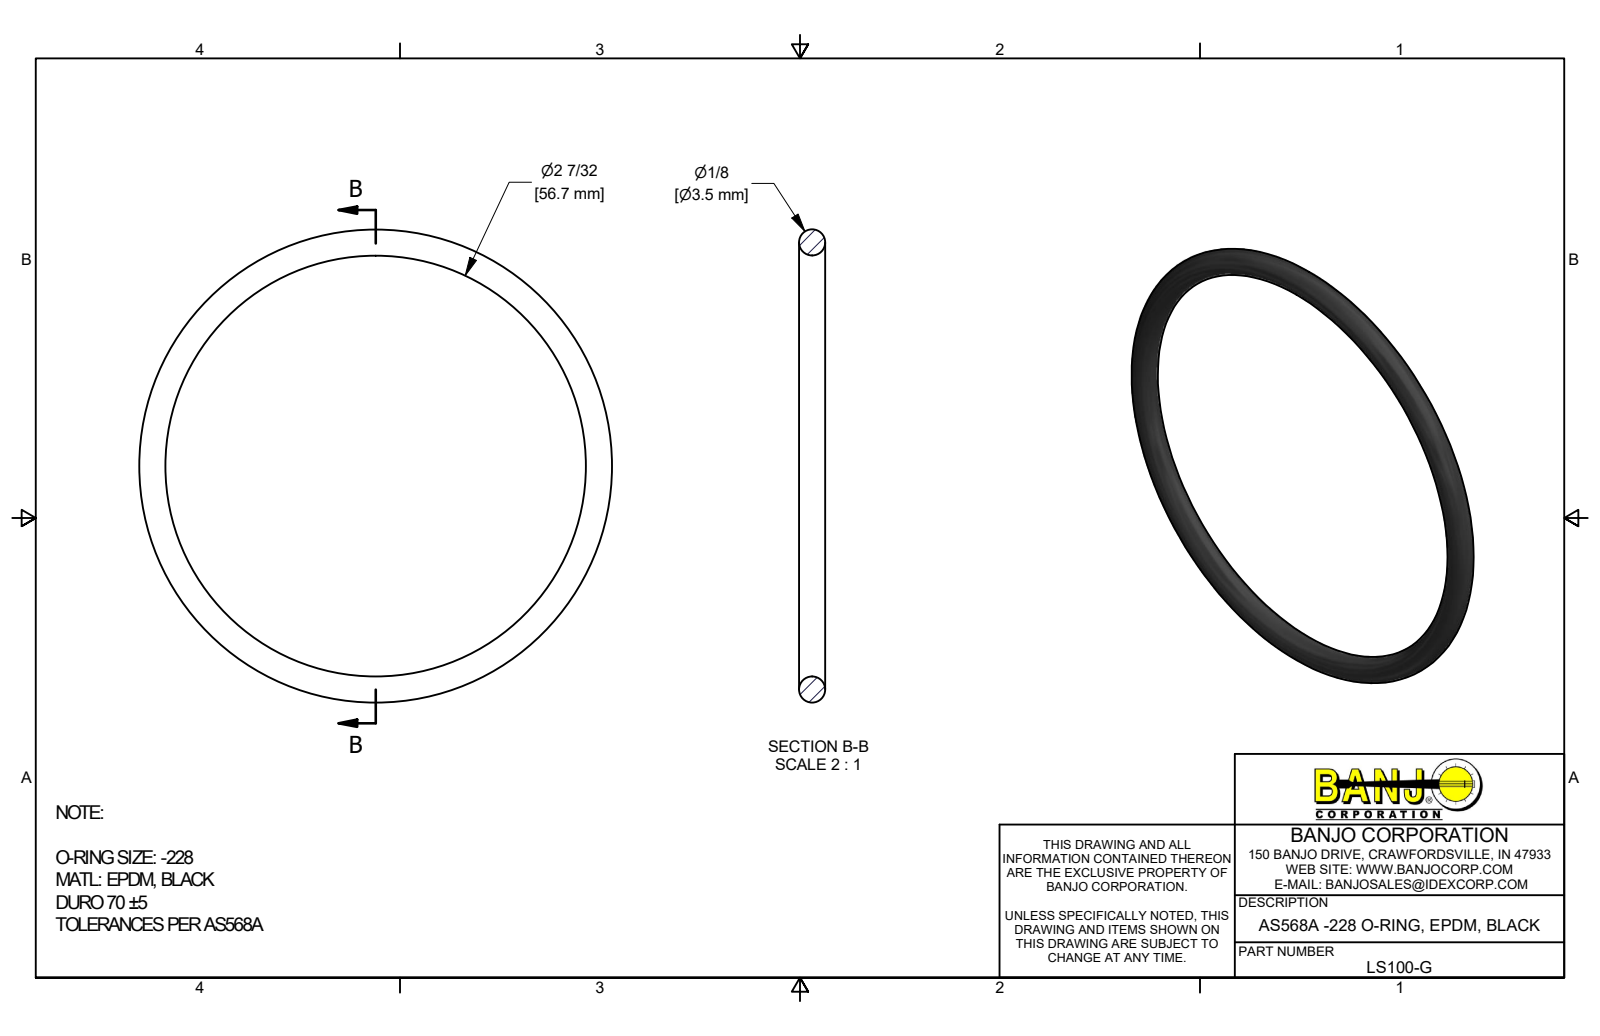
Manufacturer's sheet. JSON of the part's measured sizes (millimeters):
{"part_name": "LS100-G", "step_written_by": "Autodesk Inventor 2019 (AUTOMOTIVE_DESIGN)", "units": "millimeters", "bodies": {"solids": 1, "faces": 1, "planar": 0, "cylindrical": 0, "other": 1}, "overall_size": [63.8, 63.8, 3.5], "volume_mm3": 1850, "surface_area_mm2": 2100}
